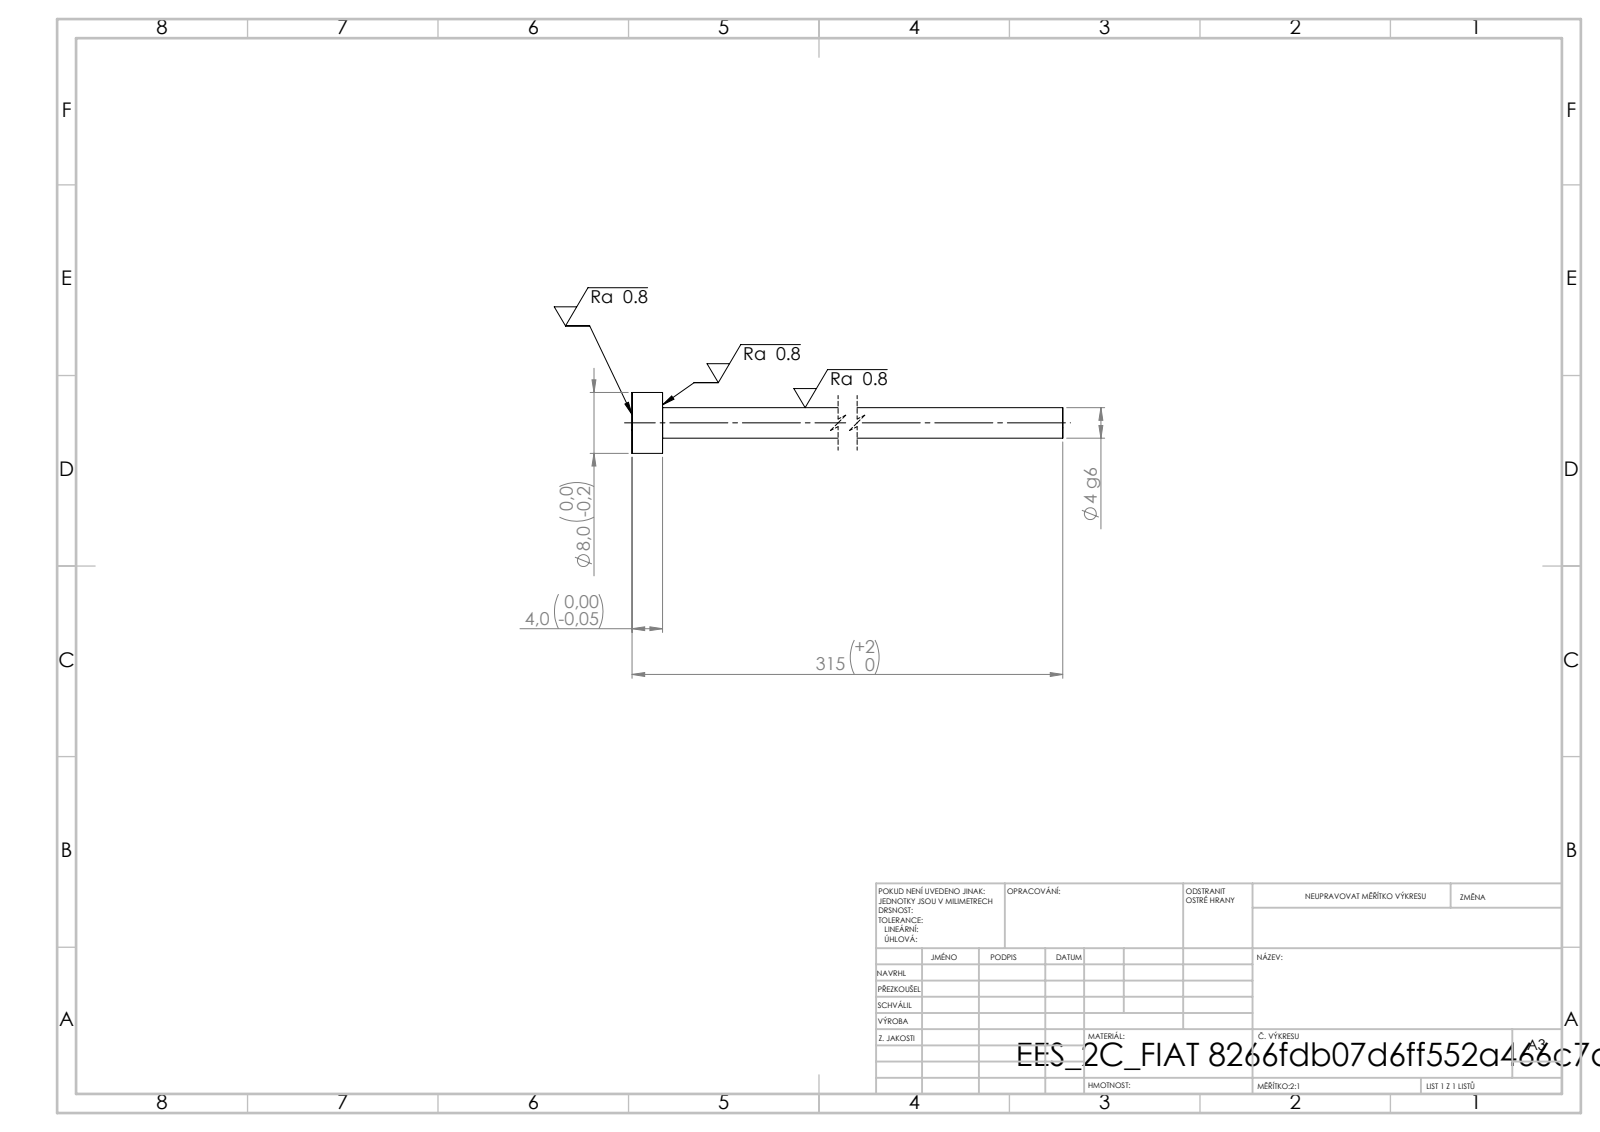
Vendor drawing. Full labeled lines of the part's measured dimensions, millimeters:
STEP written by: SolidWorks 2019 (CONFIG_CONTROL_DESIGN)
Units: millimetres
Bodies: 1 solid, 7 faces (3 planar, 4 cylindrical, 0 other)
Overall size (bounding box): 315 × 8 × 8
Volume: 4 109 mm³ · Surface area: 4 109 mm²
Round bosses / shafts (diameter × count): ⌀8 ×1, ⌀4 ×1
Main face-to-face distances: 4, 315, 311
